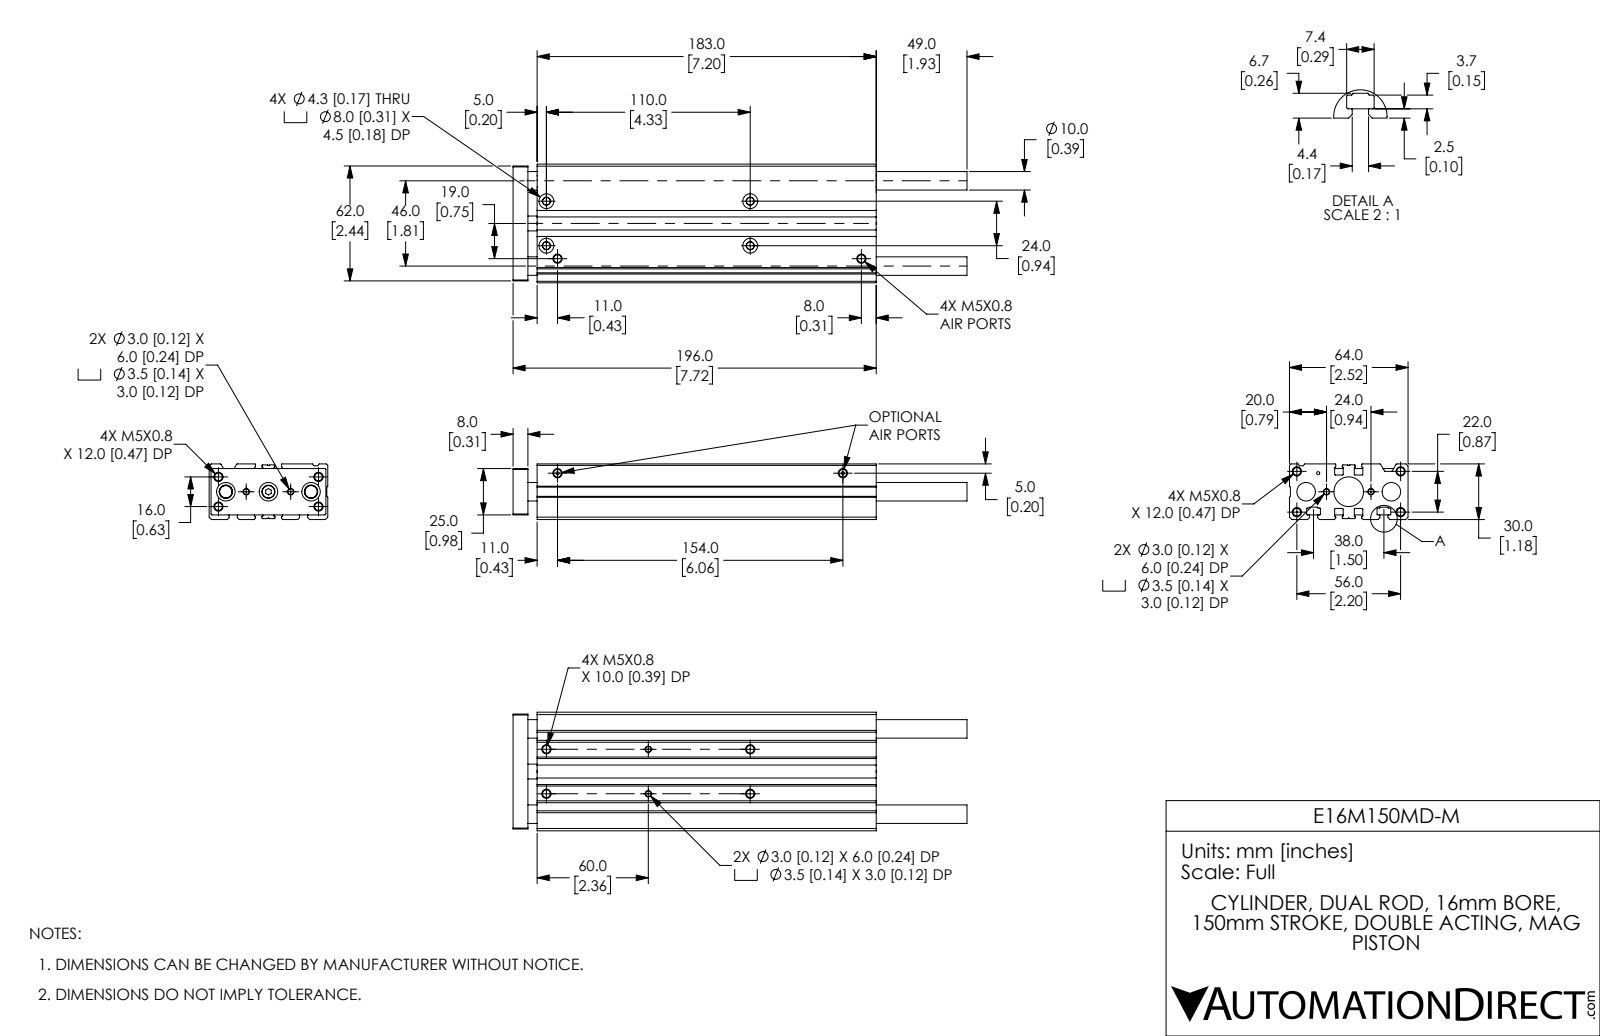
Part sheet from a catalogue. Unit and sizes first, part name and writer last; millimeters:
Units: millimetres
Overall size (bounding box): 245 × 64 × 30
Round holes (diameter × count): ⌀4.13 ×16, ⌀3 ×4, ⌀3.5 ×4, ⌀4.3 ×4, ⌀8 ×4, ⌀1.67 ×3, ⌀5 ×3, ⌀10 ×3, ⌀7.11 ×2, ⌀10 ×1, ⌀16 ×1, ⌀16 ×1
Round bosses / shafts (diameter × count): ⌀8 ×1, ⌀7.11 ×1
Partial cylindrical surfaces — rounded edges, fillets, slot ends (radius × count): R0.2 ×22, R0.4 ×20, R0.25 ×8, R0.3 ×6, R0.5 ×4
Main face-to-face distances: 30, 0.5, 6, 64, 29, 24.4, 24, 3.5, 35, 39.6
Hole centre spacings: 3.16, 8.94, 12.08, 17, 19.03, 19.42, 24, 28.16
Volume: 303 422 mm³ · Surface area: 104 136 mm²
Bodies: 5 solids, 411 faces (133 planar, 192 cylindrical, 86 other)
Part name (STEP PRODUCT): E16M150MD-M_ENDPLATE; E16M150MD-M; E16M150MD-M_BODY
STEP written by: SolidWorks 2019 (CONFIG_CONTROL_DESIGN)
